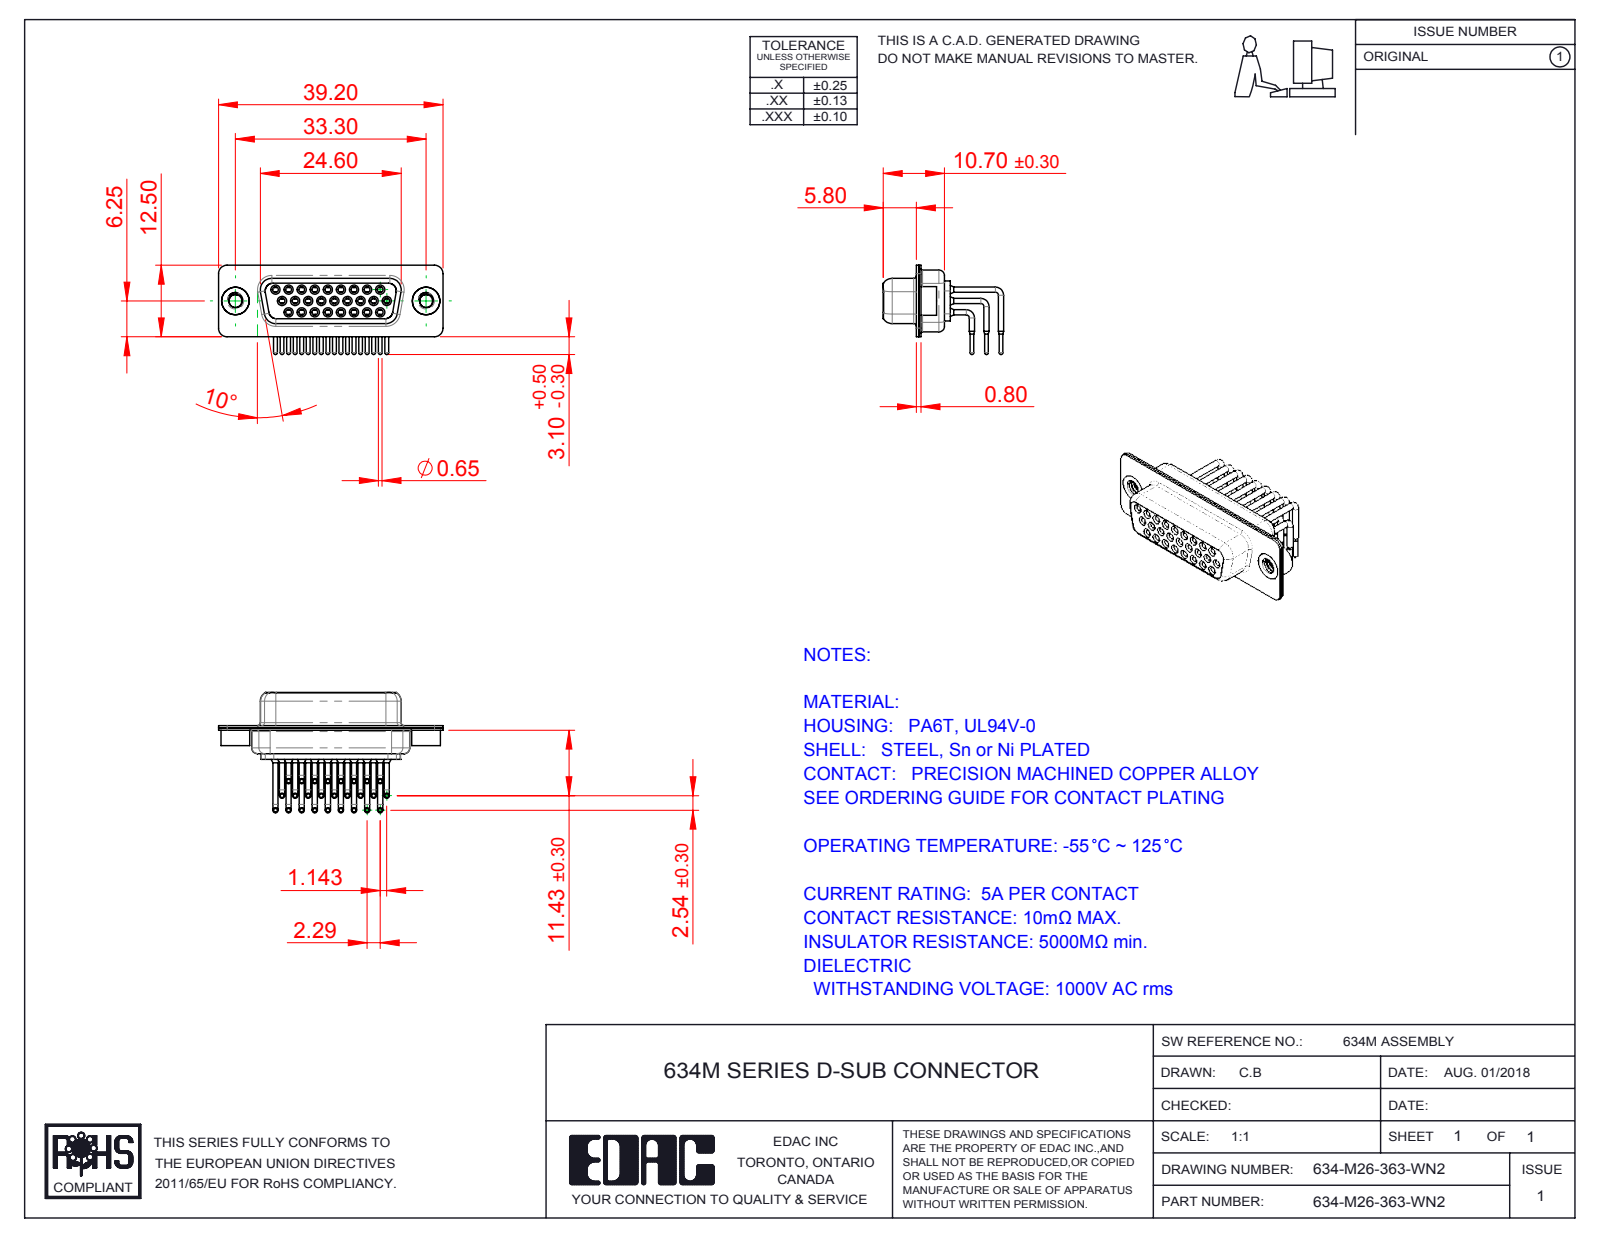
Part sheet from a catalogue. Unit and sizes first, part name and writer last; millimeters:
Units: millimetres
Overall size (bounding box): 39.2 × 21.02 × 15.6
Round holes (diameter × count): ⌀1 ×26, ⌀1.1 ×26, ⌀1.7 ×26, ⌀1.8 ×26, ⌀2 ×26, ⌀2.26 ×2, ⌀4 ×2, ⌀4.8 ×2
Round bosses / shafts (diameter × count): ⌀0.9 ×52, ⌀1.6 ×26, ⌀1.5 ×26, ⌀0.65 ×26, ⌀5 ×2, ⌀4.9 ×2, ⌀2 ×1
Partial cylindrical surfaces — rounded edges, fillets, slot ends (radius × count): R1.5 ×16, R2 ×12, R1.35 ×8, R1.6 ×8, R0.25 ×4, R0.5 ×4, R0.6 ×4, R0.65 ×4
Main face-to-face distances: 0.4, 2.3, 1.45, 8.95, 8.5, 1.9, 0.8, 6.2, 0.45, 7.05
Hole centre spacings: 3.96, 2.28, 4.57, 6.05, 2.29, 8.24, 6.86, 6.04
Volume: 2 533 mm³ · Surface area: 8 471 mm²
Bodies: 31 solids, 1657 faces (457 planar, 735 cylindrical, 465 other)
Part name (STEP PRODUCT): 634M Shell Front_26 Contacts; 634M Housing_26 Contacts; 634M Contact Row 1; 634M Shell Rear_26 Contacts (+4 more)
STEP written by: SolidWorks 2016 (CONFIG_CONTROL_DESIGN)
